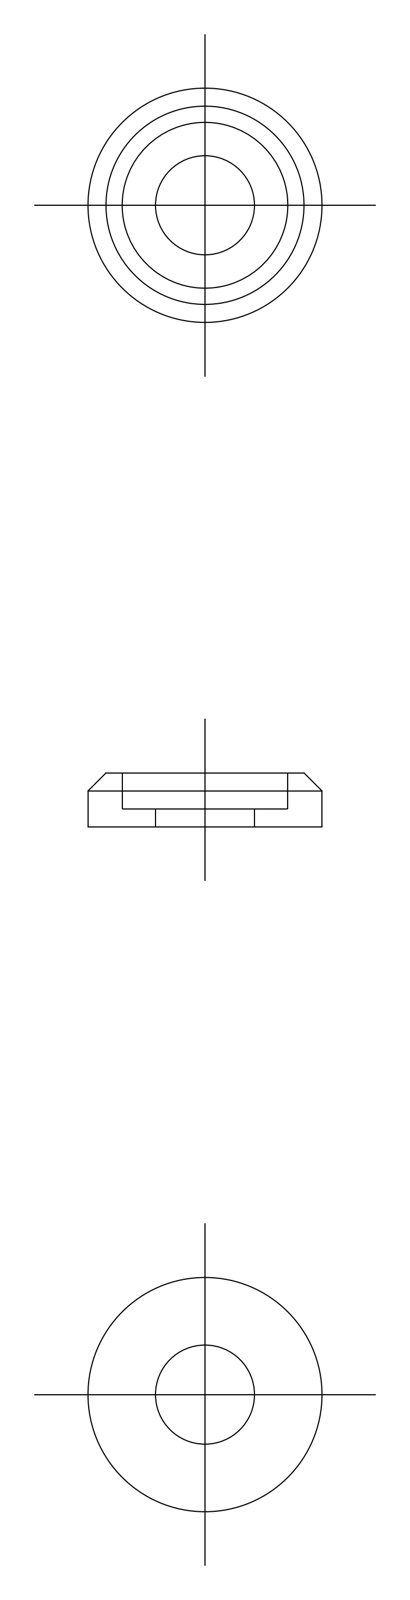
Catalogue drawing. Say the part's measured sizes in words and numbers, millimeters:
The part is named "facing ring". Its 3-D file was written by "CADfix (AUTOMOTIVE_DESIGN)". It is 1 solid with 11 faces: 0 planar, 0 cylindrical and 11 other. Overall it measures 13 by 13 by 3 millimeters. Its volume is 222 cubic millimeters and its surface area 390 square millimeters.
